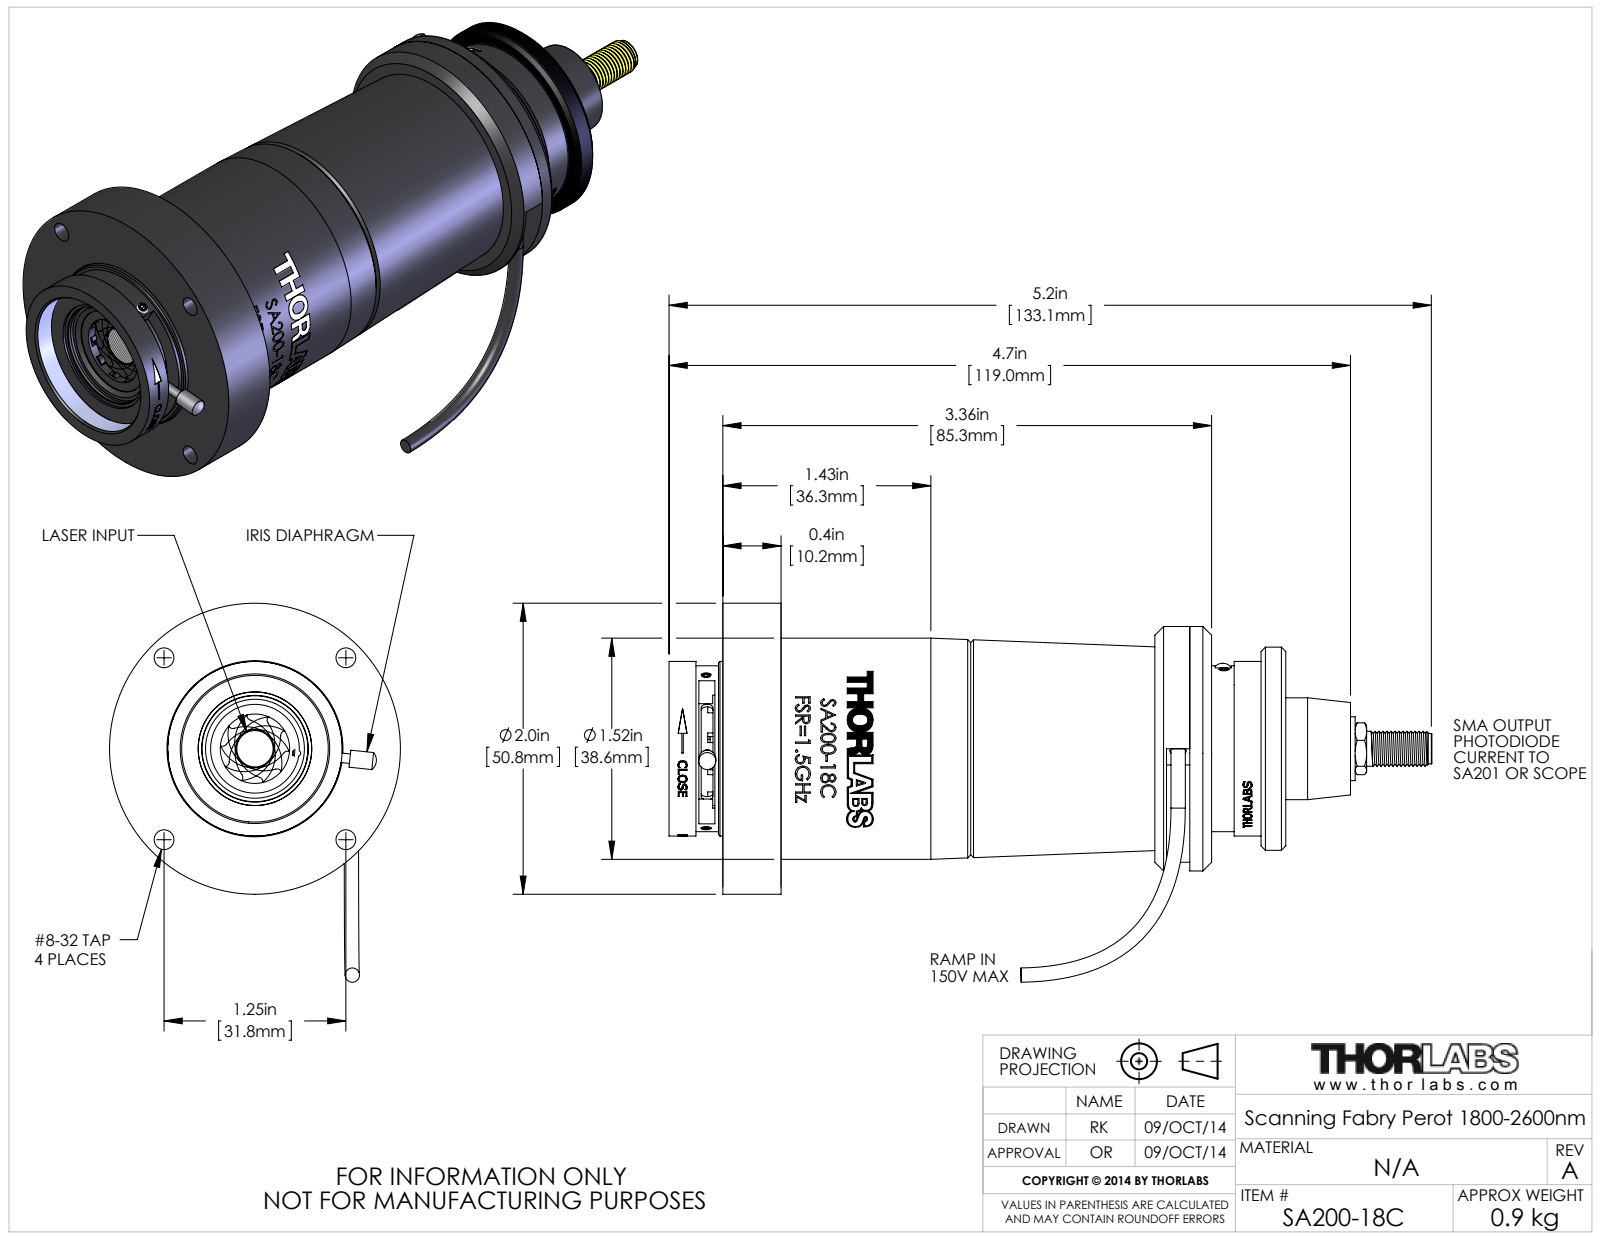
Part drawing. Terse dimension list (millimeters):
name: STN012213-E0W1
written by: SolidWorks 2014 (AUTOMOTIVE_DESIGN)
unit: mm
bodies: 42 solids, 1286 faces (616 planar, 314 cylindrical, 356 other)
size: 133.21 × 66.16 × 50.8
volume: 69 120 mm³; area: 60 602 mm²
holes: 20× ⌀1.68, 4× ⌀3.45, 2× ⌀1.09, 2× ⌀1.6, 1× ⌀1, 1× ⌀2.87, 1× ⌀4.6, 1× ⌀6.35, 1× ⌀8.26, 1× ⌀9.78, 1× ⌀10.16, 1× ⌀12.04
bosses: 20× ⌀1.52, 14× ⌀1.65, 8× ⌀1.65, 4× ⌀2.18, 2× ⌀2.98, 2× ⌀1.63, 1× ⌀50.8, 1× ⌀42.67
rounds: 20× R0.83, 20× R0.85, 20× R1.61, 20× R6.38, 20× R9.6, 2× R0.62, 2× R3.3, 2× R25.4
face distances: 81.53, 86.82, 3.81, 1.27, 98.29, 16.76, 10.16, 71.37, 88.13, 0.38
hole spacings: 14.11, 12, 8.72, 4.58, 14.83, 8.71, 14.1, 4.59
